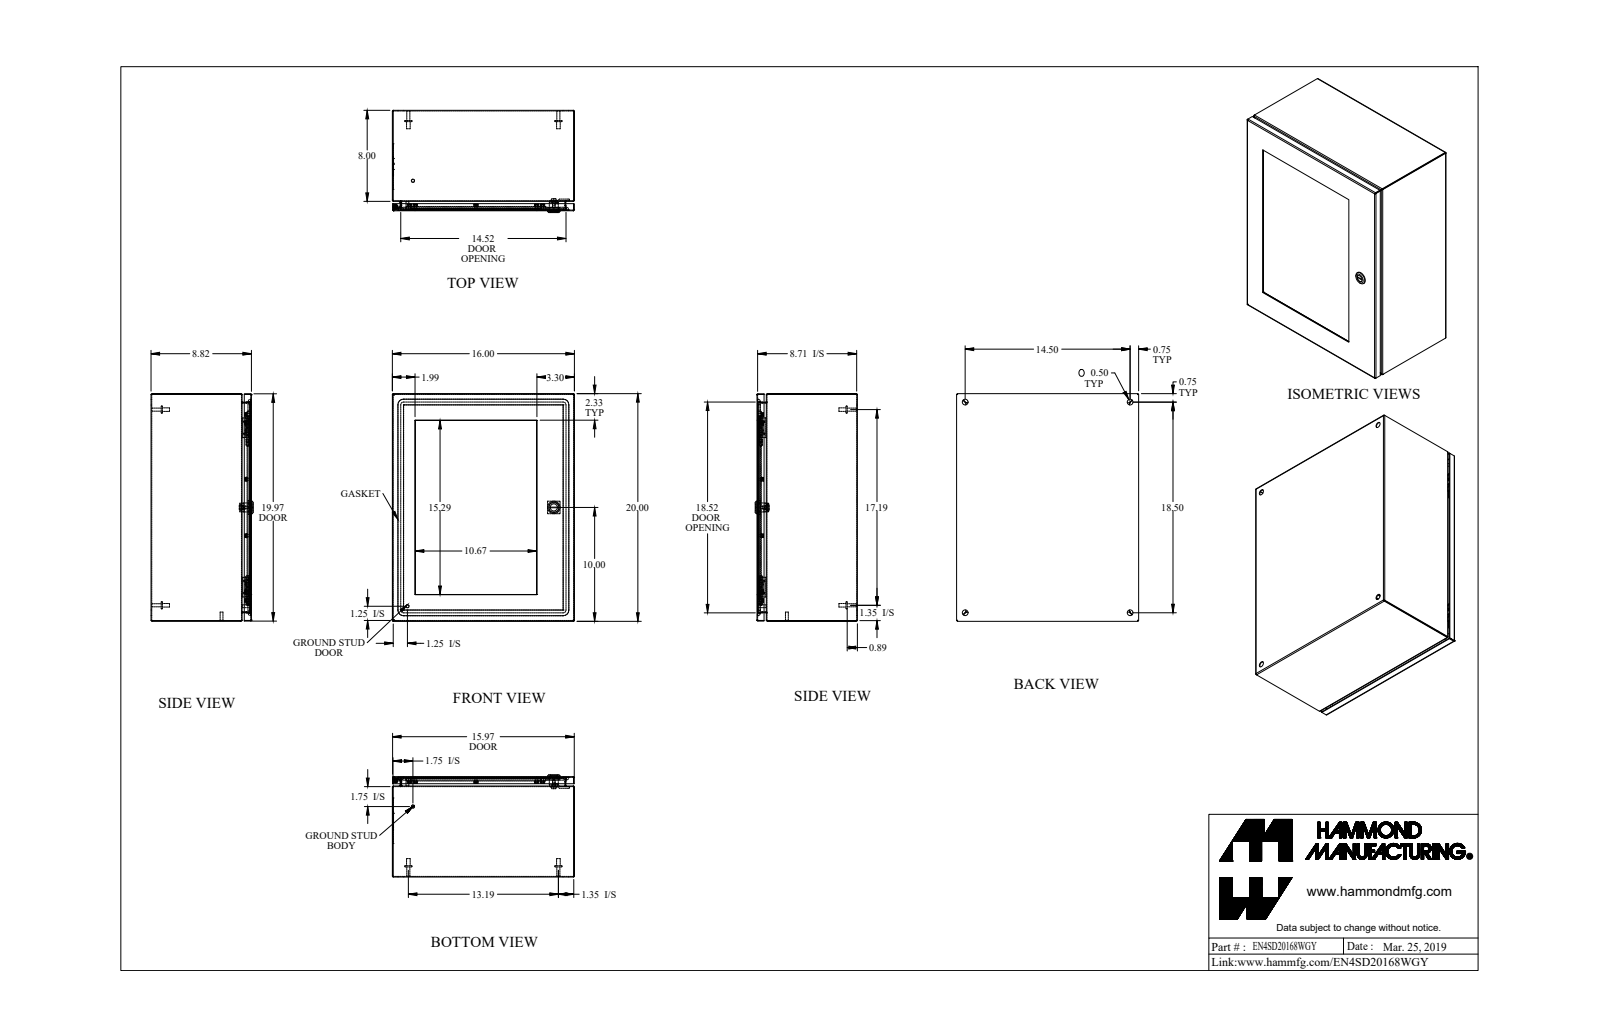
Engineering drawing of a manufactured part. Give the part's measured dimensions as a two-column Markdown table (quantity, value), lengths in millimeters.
| quantity | value |
| --- | --- |
| part name | EN4SD20168WGY_Default |
| STEP written by | SolidWorks 2019 (CONFIG_CONTROL_DESIGN) |
| units | millimeters |
| bodies | 58 solids, 1197 faces (594 planar, 369 cylindrical, 234 other) |
| overall size | 508 × 406.4 × 228.1 |
| volume | 2 040 000 mm³ |
| surface area | 1 994 000 mm² |
| round holes (diameter × count) | 3.3 × 14, 6.4 × 14, 12.7 × 4, 4.4 × 1, 5.9 × 1, 6.1 × 1, 6.1 × 1, 15.9 × 1, 19.9 × 1 |
| round bosses / shafts (diameter × count) | 5.7 × 15, 9.3 × 14, 4.2 × 14, 15.9 × 4, 8 × 4, 6.9 × 4, 7.1 × 2, 6.4 × 2 |
| partial cylindrical surfaces (radius × count) | 0.7 × 21, 2.2 × 21, 6.4 × 16, 3.2 × 10, 482.6 × 8, 0.2 × 4, 0.4 × 4, 1.6 × 4 |
| main face-to-face distances | 1.4, 222.6, 221.2, 405, 506.6, 6.4, 214.8, 216.3, 403.5, 406.4 |
| hole center spacings | 125.9, 396.5, 396.6, 135.5, 251.9, 318.8, 322.9, 323 |
